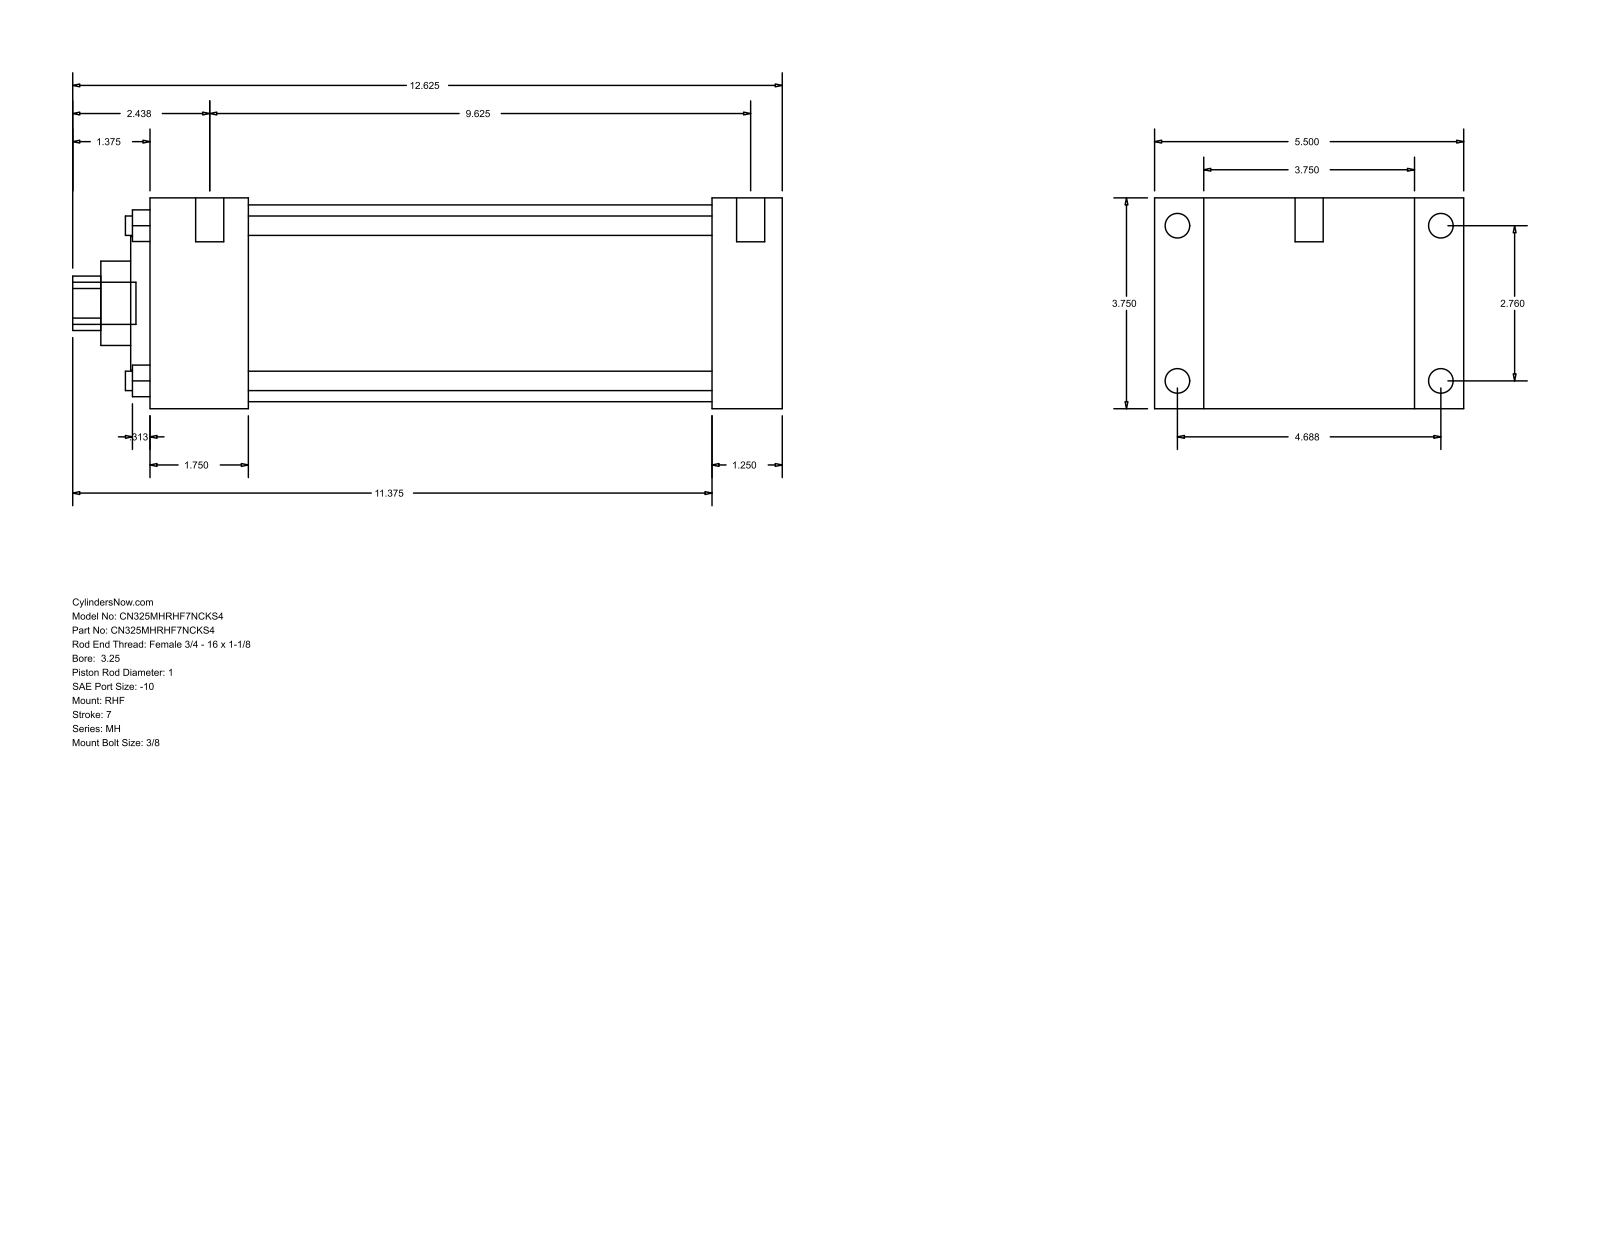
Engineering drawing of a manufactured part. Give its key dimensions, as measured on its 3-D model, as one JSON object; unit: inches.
{"part_name": "MH_RHF__0325_1", "step_written_by": "GSSL Pune (CONFIG_CONTROL_DESIGN)", "units": "inches", "bodies": {"solids": 0, "faces": 90, "planar": 61, "cylindrical": 29, "other": 0}, "overall_size": [12.625, 5.5, 3.75], "round_holes": [[0.345, 4], [1, 1], [1.5, 1], [2.375, 1], [3.5, 1]], "round_bosses_or_shafts": [[0.438, 4], [0.219, 4], [0.5, 2], [0.75, 1]], "partial_cylinders_radius": [[0.484, 1]], "face_to_face_distances": [3.75, 1.25, 0.875, 4.625, 10, 11.25, 5.5, 1.75, 8.25, 9.5], "hole_center_spacings": [1.952, 2.76, 3.903]}
